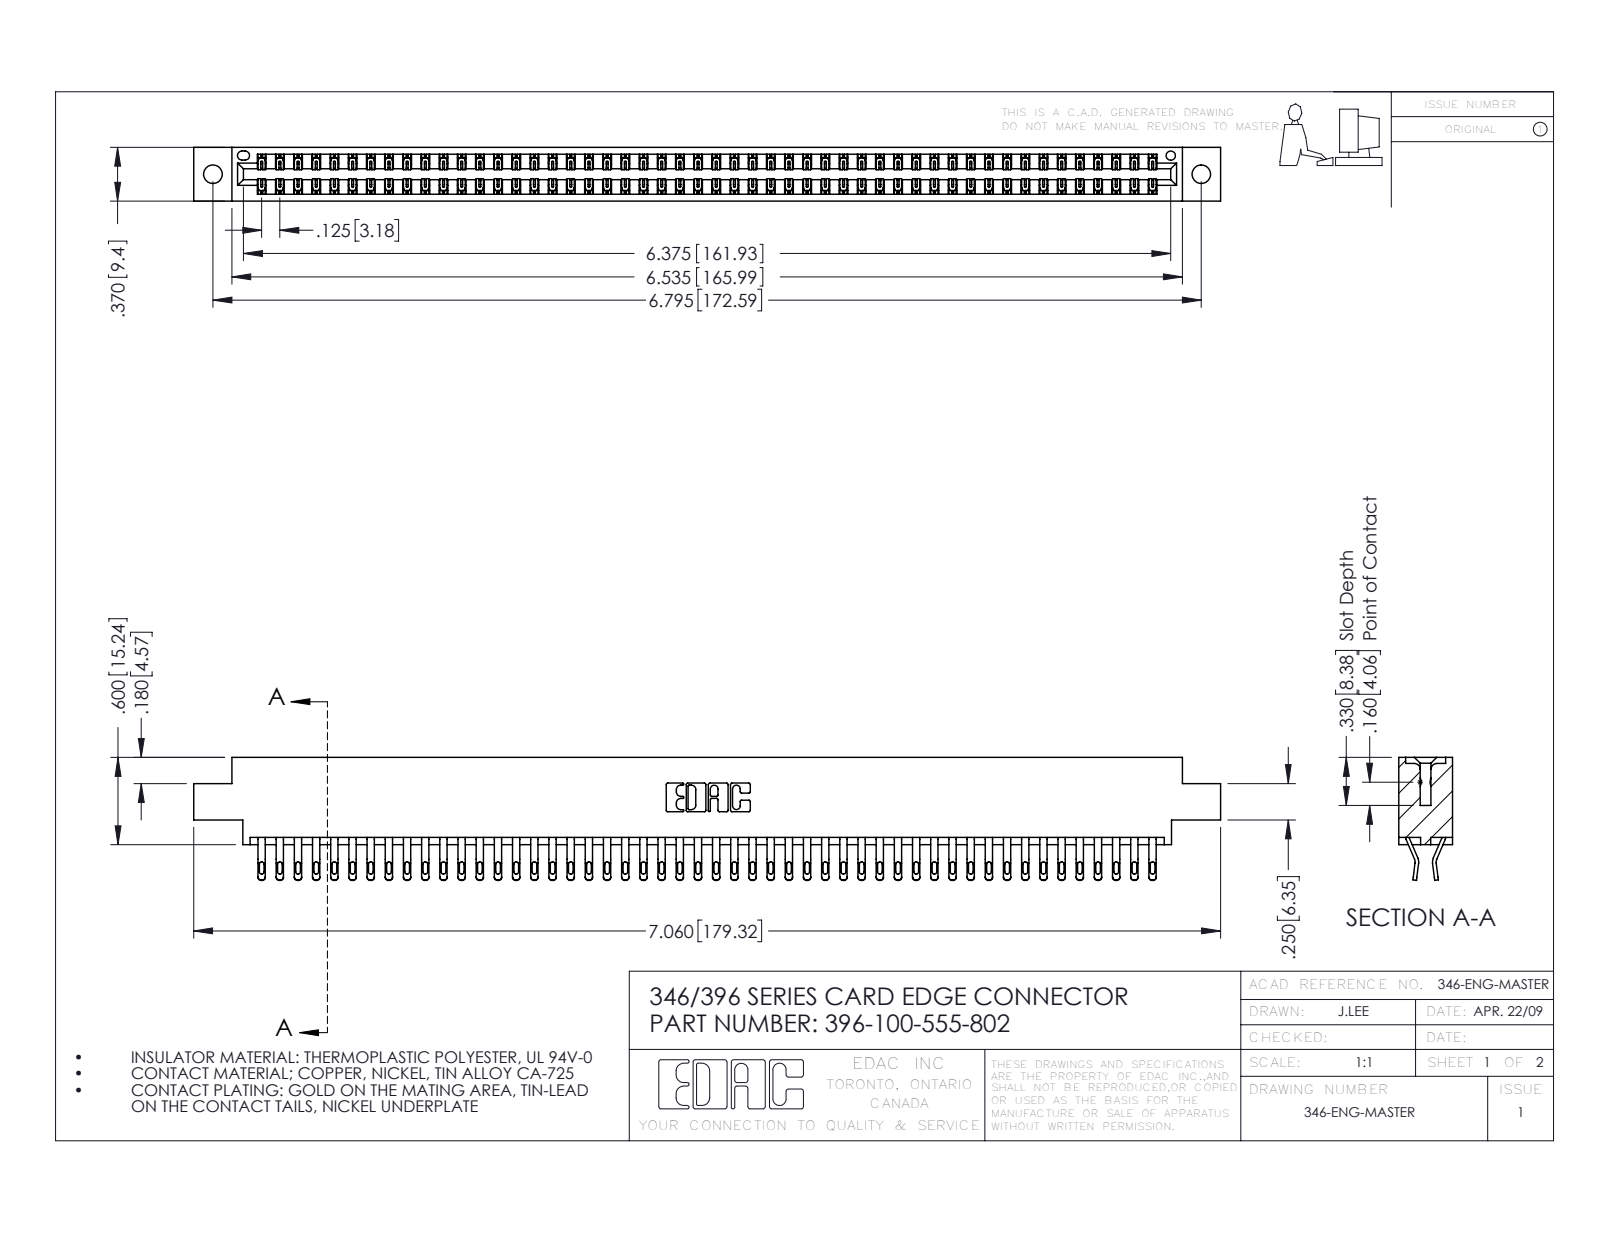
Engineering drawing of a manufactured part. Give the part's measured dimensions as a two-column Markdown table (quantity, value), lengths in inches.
| quantity | value |
| --- | --- |
| part name | 346 Part_0.170 Offset - 0.128 Dia; 345-292-001_555 Tail; 396-100-555-802 |
| STEP written by | SolidWorks 2016 (CONFIG_CONTROL_DESIGN) |
| units | inches |
| bodies | 101 solids, 5926 faces (3380 planar, 2546 cylindrical, 0 other) |
| overall size | 7.06 × 0.845 × 0.37 |
| volume | 1.077 in³ |
| surface area | 39.26 in² |
| round holes (diameter × count) | 0.128 × 2, 0.064 × 1 |
| partial cylindrical surfaces (radius × count) | 0.016 × 200, 0.02 × 200, 0.006 × 150, 0.01 × 22, 0.007 × 6, 0.031 × 6, 0.026 × 3, 0.01 × 2 |
| main face-to-face distances | 0.048, 0.322, 0.37, 0.25, 0.025, 0.072, 0.298, 0.275, 0.148, 0.222 |
| hole center spacings | 0.246, 6.586, 6.795 |
